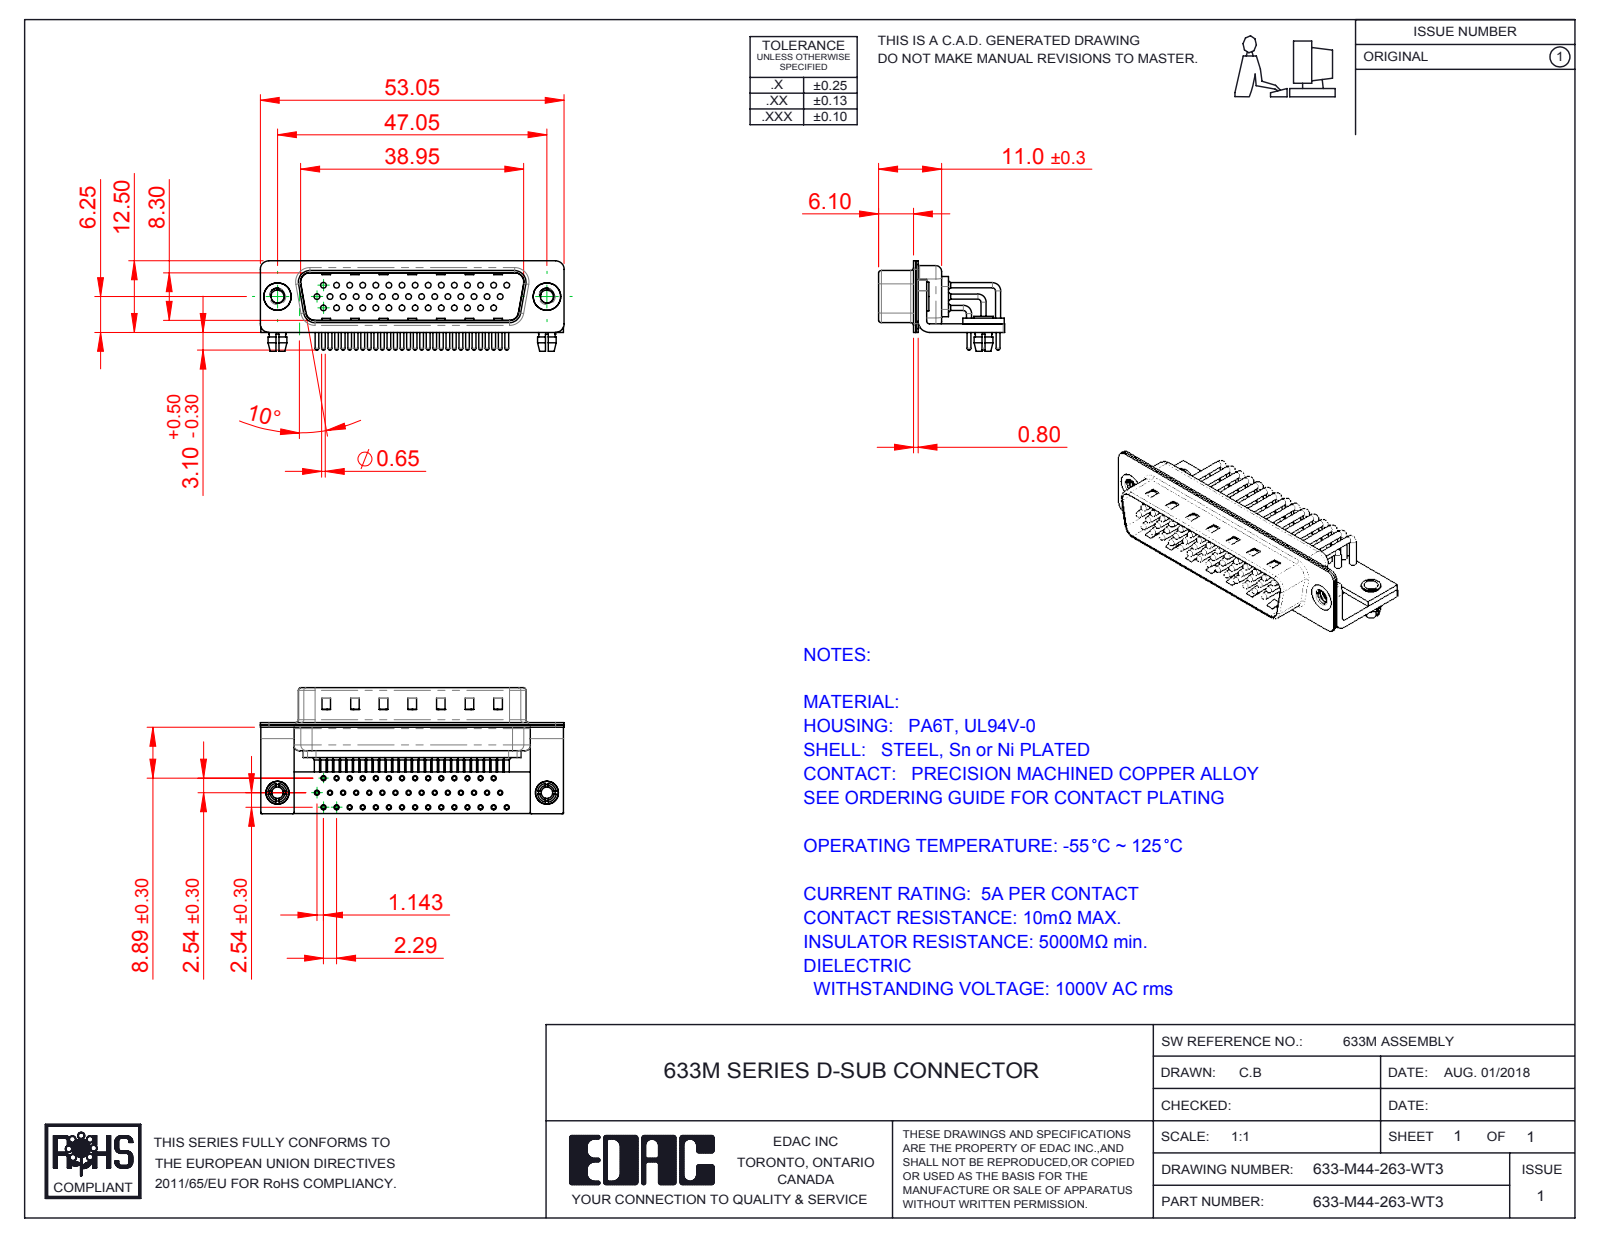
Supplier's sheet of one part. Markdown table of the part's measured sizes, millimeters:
| quantity | value |
| --- | --- |
| part name | 633M Shell Front_44 Contacts; 633M Board Lock; 633M Contact Row 2; 633M 4-40 Threaded Rivet_Stabilizer (+7 more) |
| STEP written by | SolidWorks 2016 (CONFIG_CONTROL_DESIGN) |
| units | millimeters |
| bodies | 54 solids, 5446 faces (3061 planar, 1863 cylindrical, 522 other) |
| overall size | 53.05 × 22 × 15.8 |
| volume | 3 800 mm³ |
| surface area | 11 849 mm² |
| round holes (diameter × count) | 2 × 46, 0.9 × 44, 1 × 44, 1.7 × 44, 2.26 × 2, 2.5 × 2, 3.2 × 2, 4 × 2, 4.8 × 2 |
| round bosses / shafts (diameter × count) | 0.9 × 45, 1.5 × 44, 0.65 × 44, 5 × 2, 4.9 × 2, 4 × 2, 3.4 × 2, 3.3 × 2 |
| partial cylindrical surfaces (radius × count) | 1.01 × 44, 0.25 × 16, 1.5 × 16, 2 × 13, 0.5 × 9, 1.6 × 8, 0.6 × 4, 0.65 × 4 |
| main face-to-face distances | 0.4, 1.5, 0.85, 1.25, 1, 1.9, 10.4, 0.8, 9.55, 8.3 |
| hole center spacings | 2.28, 2.29, 4.57, 6.86, 3.96, 11.43, 8.24, 16 |
